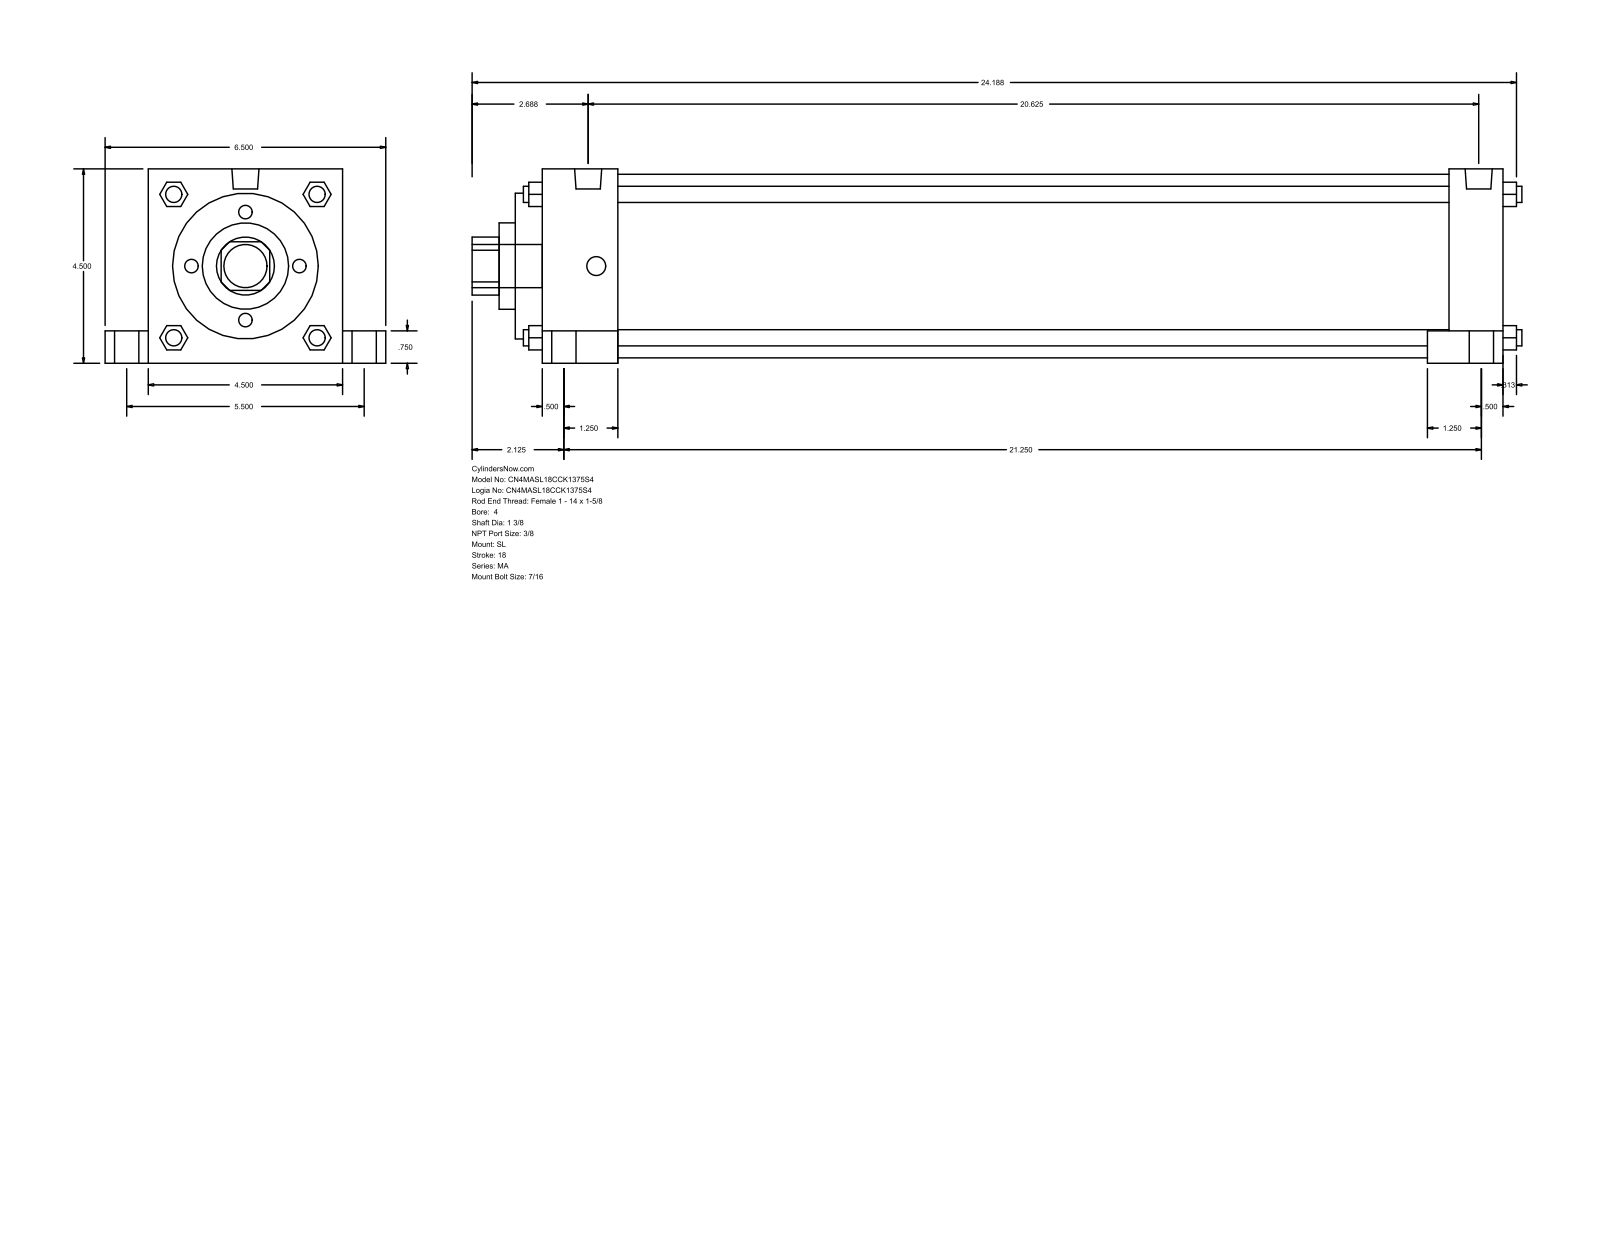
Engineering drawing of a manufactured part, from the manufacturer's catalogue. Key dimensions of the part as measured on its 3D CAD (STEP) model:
Part name (STEP PRODUCT): MA_SL__0400_1.375
STEP written by: GSSL Pune (CONFIG_CONTROL_DESIGN)
Units: millimetres
Bodies: 0 solids, 150 faces (113 planar, 37 cylindrical, 0 other)
Overall size (bounding box): 617.54 × 165.1 × 114.3
Round holes (diameter × count): ⌀34.92 ×1, ⌀50.8 ×1, ⌀85.72 ×1, ⌀107.95 ×1
Round bosses / shafts (diameter × count): ⌀20.64 ×4, ⌀14.29 ×4, ⌀11.11 ×4, ⌀9.53 ×4, ⌀15.93 ×2, ⌀25.4 ×1
Partial cylindrical surfaces — rounded edges, fillets, slot ends (radius × count): R17.06 ×1
Main face-to-face distances: 114.3, 565.15, 488.95, 581.02, 15.87, 60.32, 44.45, 520.7, 549.27, 533.4
